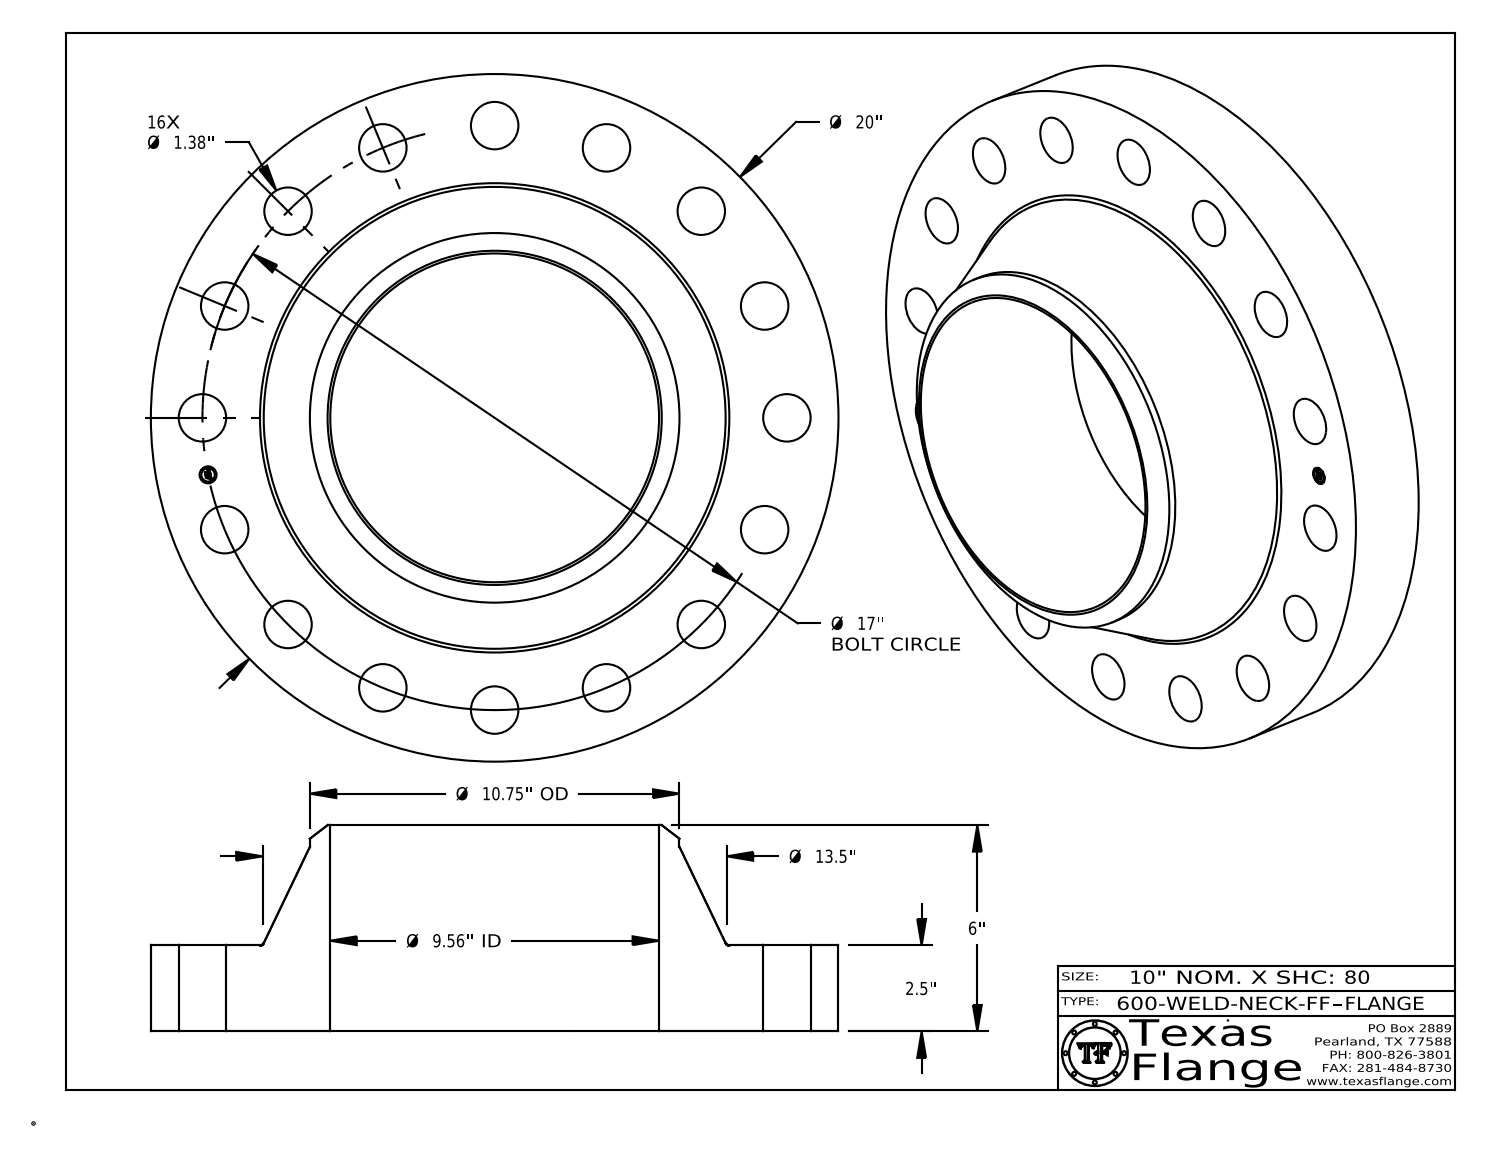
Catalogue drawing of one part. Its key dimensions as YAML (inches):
part_name: "600-WELD-NECK-FF"
step_written_by: "CATIA V5 STEP AP214 (AUTOMOTIVE_DESIGN)"
units: inches
bodies: {solids: 1, faces: 432, planar: 368, cylindrical: 58, other: 6}
overall_size: [20, 20, 6]
volume: 681.4
surface_area: 1028
round_holes:
  - {diameter: 1.38, count: 16}
  - {diameter: 0.495, count: 1}
  - {diameter: 9.562, count: 1}
round_bosses_or_shafts:
  - {diameter: 0.03, count: 8}
  - {diameter: 20, count: 1}
  - {diameter: 10.75, count: 1}
  - {diameter: 0.39, count: 1}
face_to_face_distances: [2.5, 6, 3.5, 2.485, 0.015, 3.515, 0.148, 0.145, 0.027, 0.096]
hole_center_spacings: [3.317, 14.135, 8.5, 6.506, 12.021, 9.444, 9.445, 15.706]
